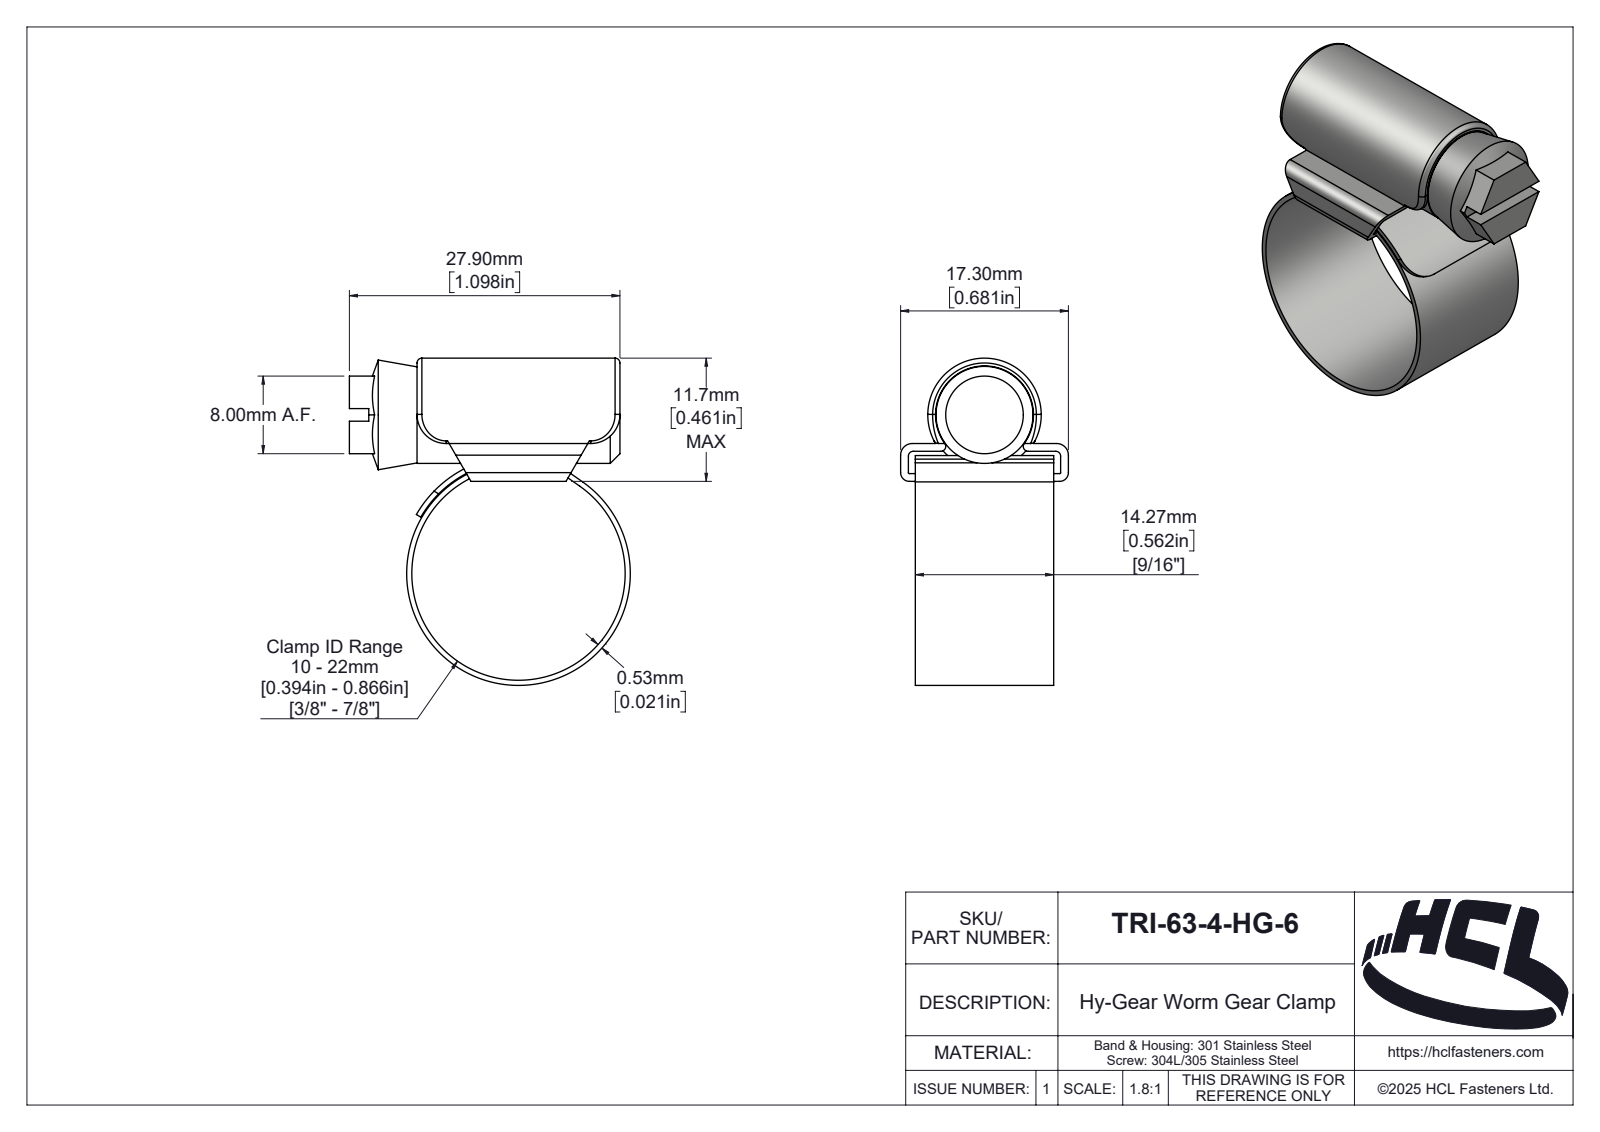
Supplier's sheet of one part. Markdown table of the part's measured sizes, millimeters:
| quantity | value |
| --- | --- |
| part name | TRI-50-0-HG-6 |
| STEP written by | SolidWorks 2025 (AUTOMOTIVE_DESIGN) |
| units | millimeters |
| bodies | 3 solids, 189 faces (39 planar, 89 cylindrical, 61 other) |
| overall size | 33.73 × 28.97 × 17.3 |
| volume | 3 422 mm³ |
| surface area | 5 272 mm² |
| round holes (diameter × count) | 22 × 1 |
| round bosses / shafts (diameter × count) | 23.06 × 1, 10 × 1 |
| partial cylindrical surfaces (radius × count) | 0.5 × 6, 3 × 4, 0.1 × 2, 0.9 × 2, 1.2 × 2, 0.46 × 1, 1.89 × 1, 2 × 1 |
| main face-to-face distances | 0.8, 3.1, 2.3, 3.9, 0.53, 27.9, 1.52, 15.78, 14.26, 16.5 |
